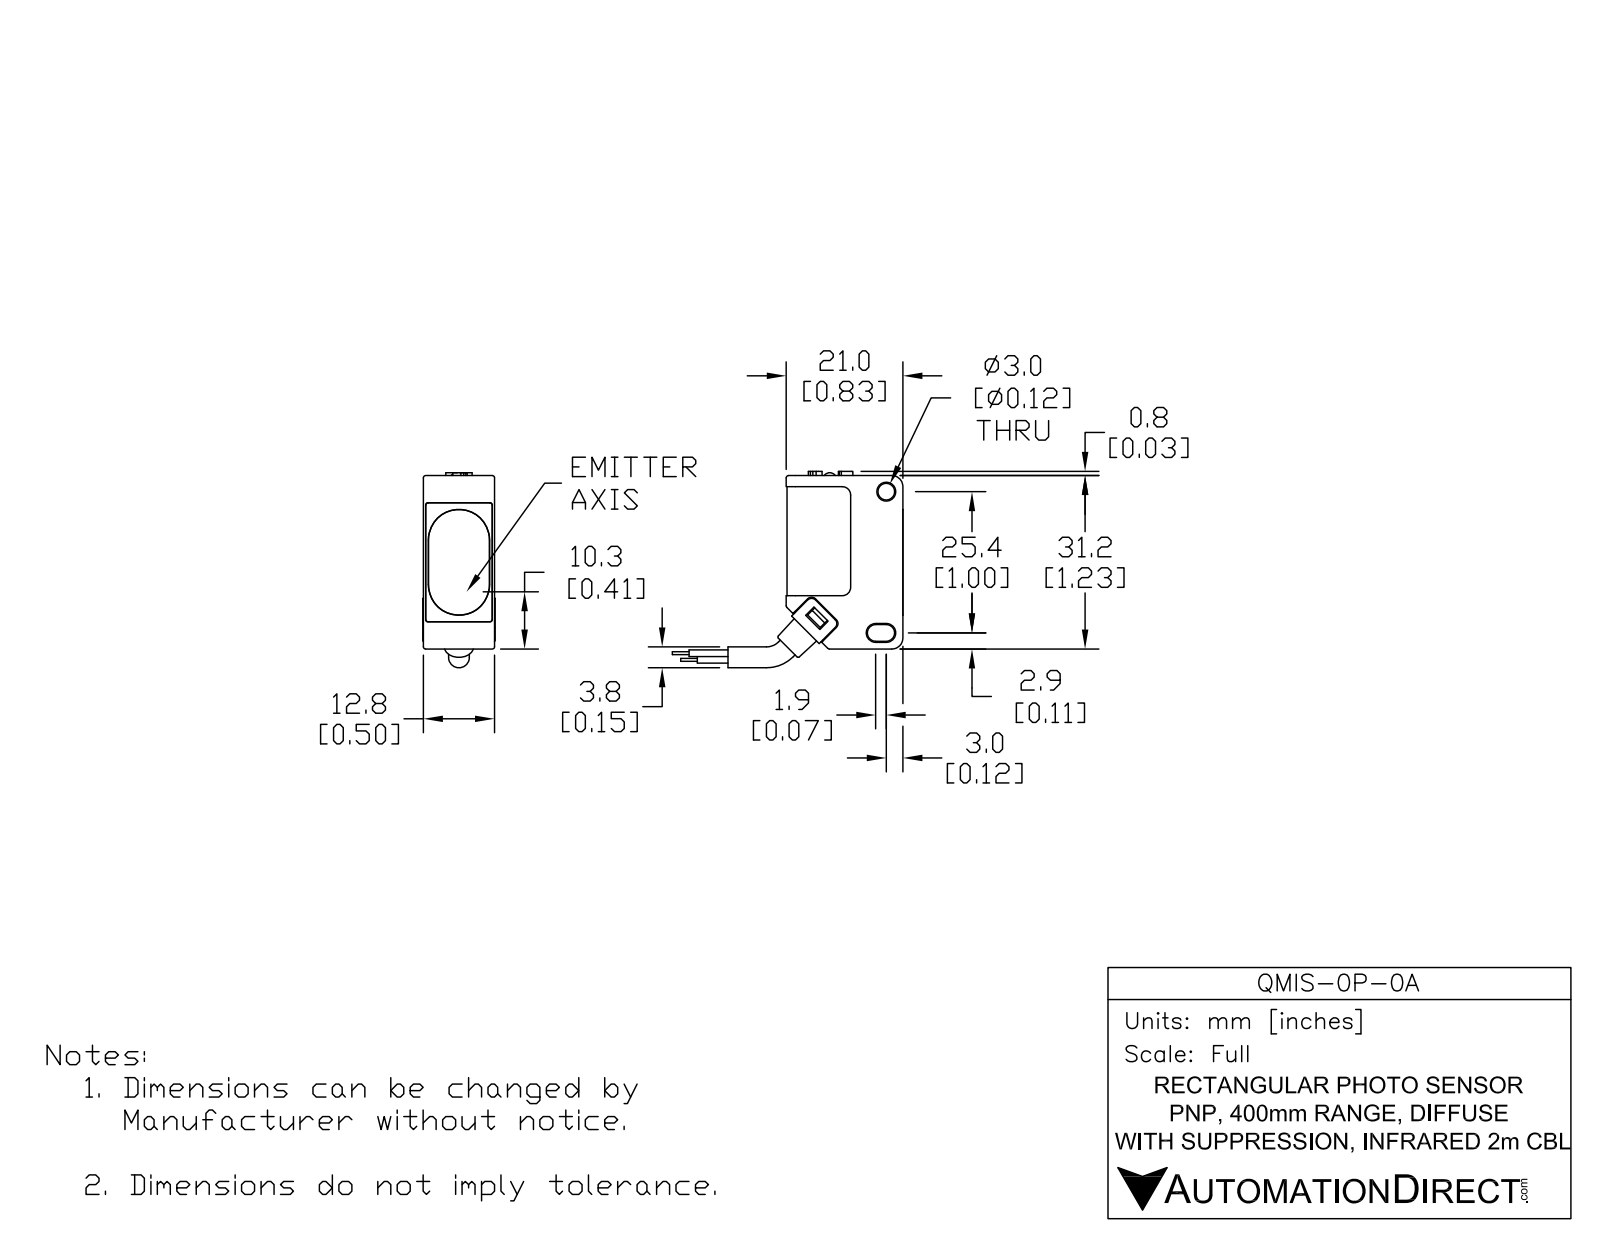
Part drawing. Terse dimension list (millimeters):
name: QMIS-0P-0A
written by: SolidWorks 2017 (AUTOMOTIVE_DESIGN)
unit: mm
bodies: 9 solids, 248 faces (132 planar, 92 cylindrical, 24 other)
size: 81.1 × 26.2 × 13
volume: 7 620 mm³; area: 5 385 mm²
holes: 1× ⌀3, 1× ⌀3.8, 1× ⌀4.4, 1× ⌀5.7, 1× ⌀7.2
bosses: 1× ⌀3.1, 1× ⌀2.8
rounds: 13× R0.4, 8× R1, 7× R1.5, 4× R0.5, 4× R0.6, 4× R4.5, 2× R0.9, 2× R1.7
face distances: 12.6, 1, 0.5, 0.4, 12.8, 3.5, 12.4, 12.2, 2.5, 12.5
